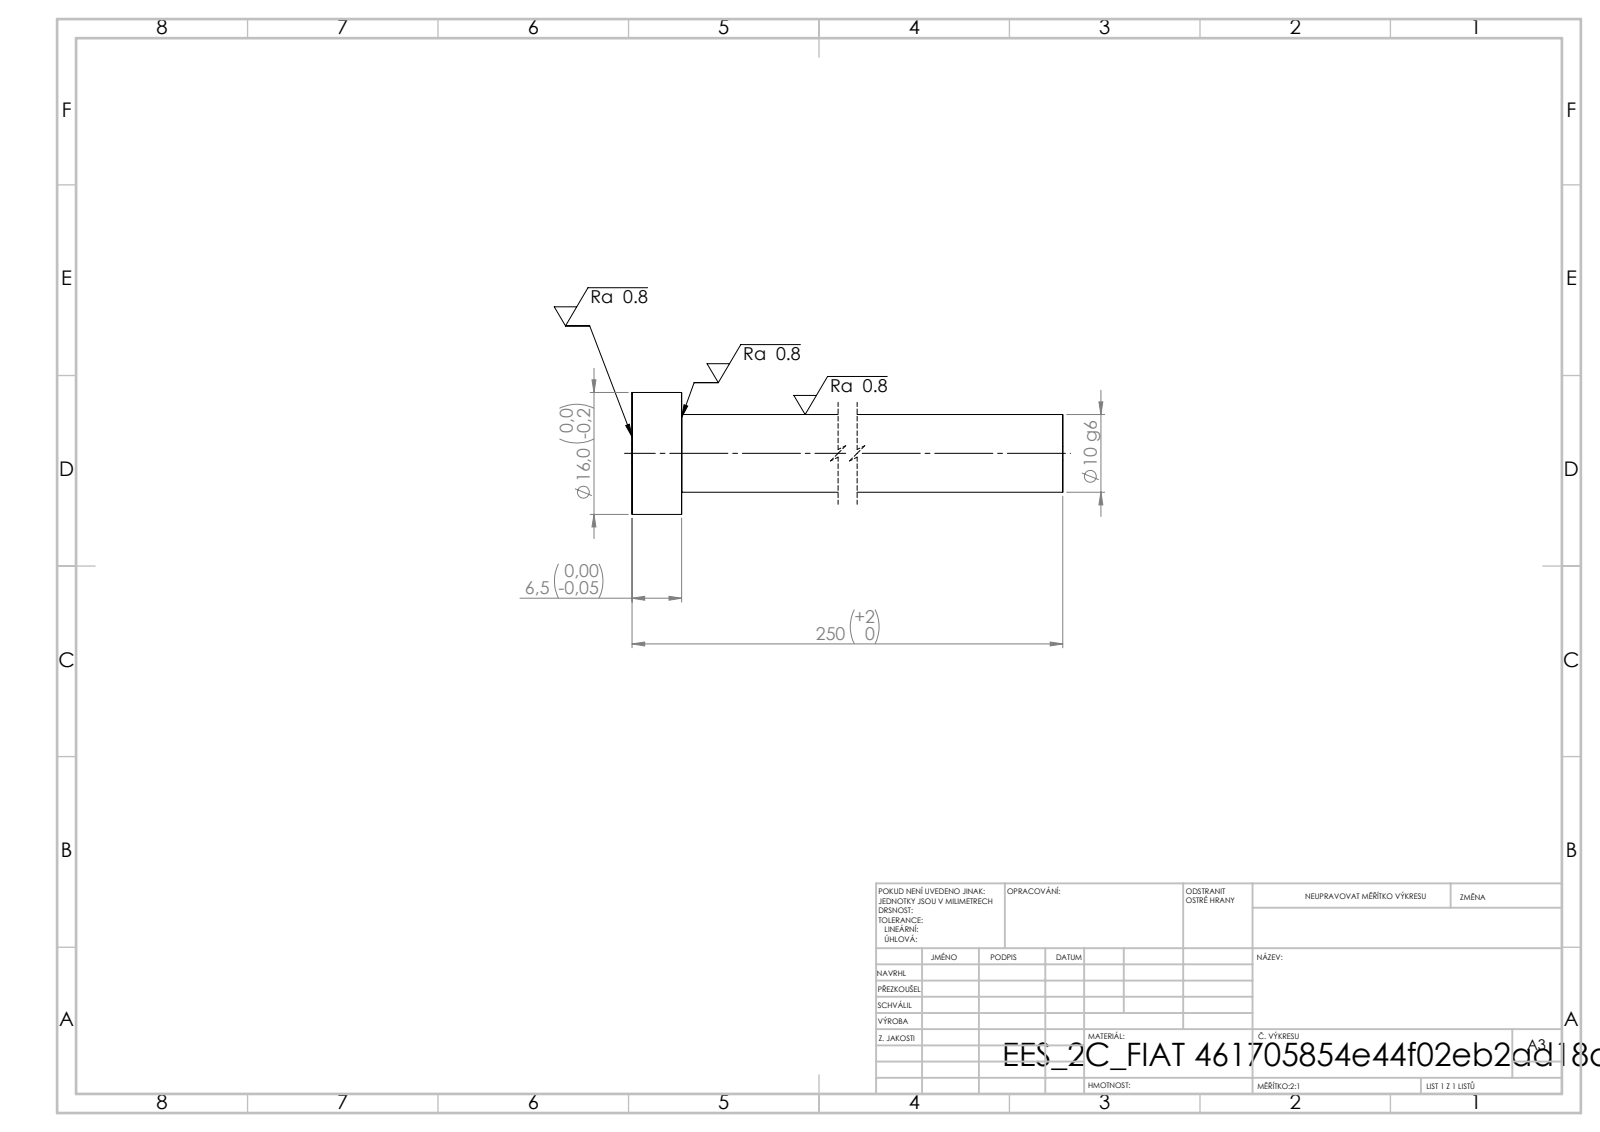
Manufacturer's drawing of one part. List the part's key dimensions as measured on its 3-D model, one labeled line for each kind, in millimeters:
STEP written by: SolidWorks 2019 (CONFIG_CONTROL_DESIGN)
Units: millimetres
Bodies: 1 solid, 7 faces (3 planar, 4 cylindrical, 0 other)
Overall size (bounding box): 250 × 16 × 16
Volume: 21 204 mm³ · Surface area: 8 532 mm²
Round bosses / shafts (diameter × count): ⌀16 ×1, ⌀10.2 ×1
Main face-to-face distances: 6.5, 250, 243.5
